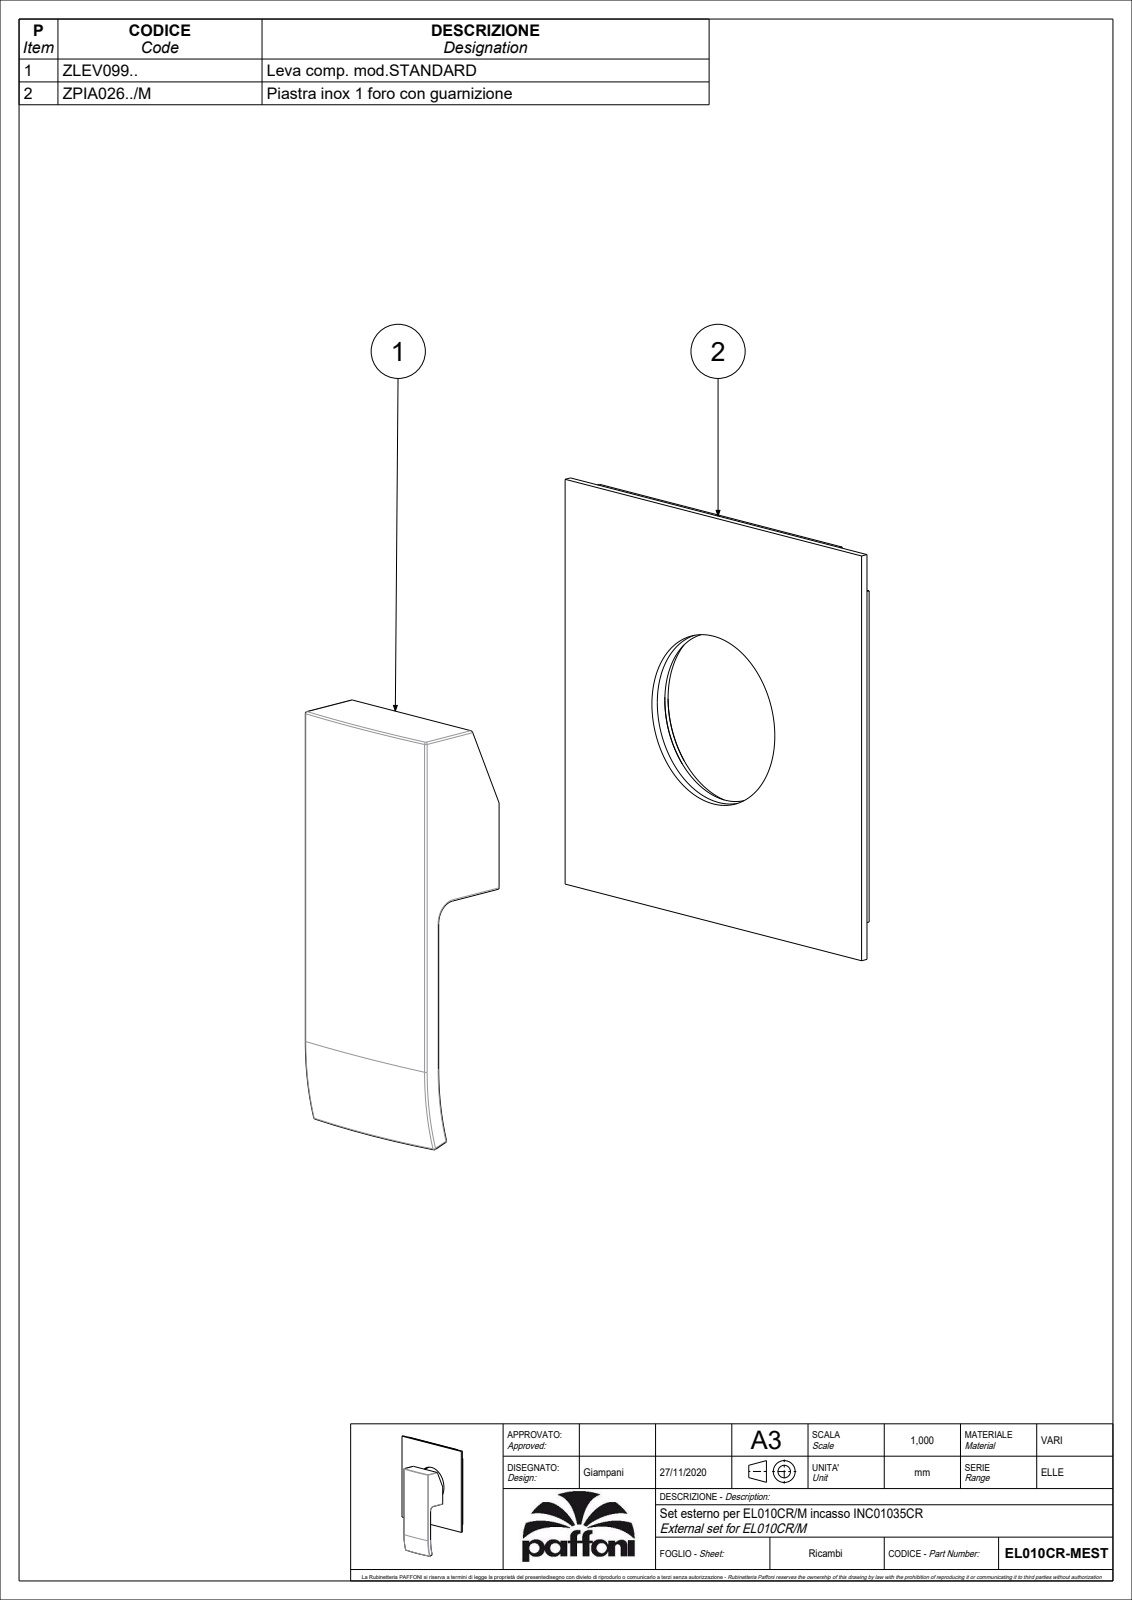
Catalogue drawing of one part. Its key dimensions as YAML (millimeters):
part_name: "EL010CR-MEST"
step_written_by: "CREO PARAMETRIC BY PTC INC, 2020044 (CONFIG_CONTROL_DESIGN)"
units: millimeters
bodies: {solids: 2, faces: 187, planar: 81, cylindrical: 61, other: 45}
overall_size: [143.38, 110, 37.5]
volume: 59193
surface_area: 45576
round_holes:
  - {diameter: 3, count: 1}
  - {diameter: 3.3, count: 1}
  - {diameter: 5.5, count: 1}
  - {diameter: 7.8, count: 1}
  - {diameter: 45.6, count: 1}
  - {diameter: 47.6, count: 1}
  - {diameter: 51.1, count: 1}
round_bosses_or_shafts:
  - {diameter: 54.6, count: 1}
  - {diameter: 7.6, count: 1}
  - {diameter: 5, count: 1}
partial_cylinders:
  - {radius: 1.5, count: 14}
  - {radius: 0.5, count: 10}
  - {radius: 2, count: 4}
  - {radius: 300, count: 2}
  - {radius: 2.25, count: 1}
face_to_face_distances: [2, 0.8, 2.8, 45, 30, 29.2, 27.2, 32.5, 77.5, 110]
